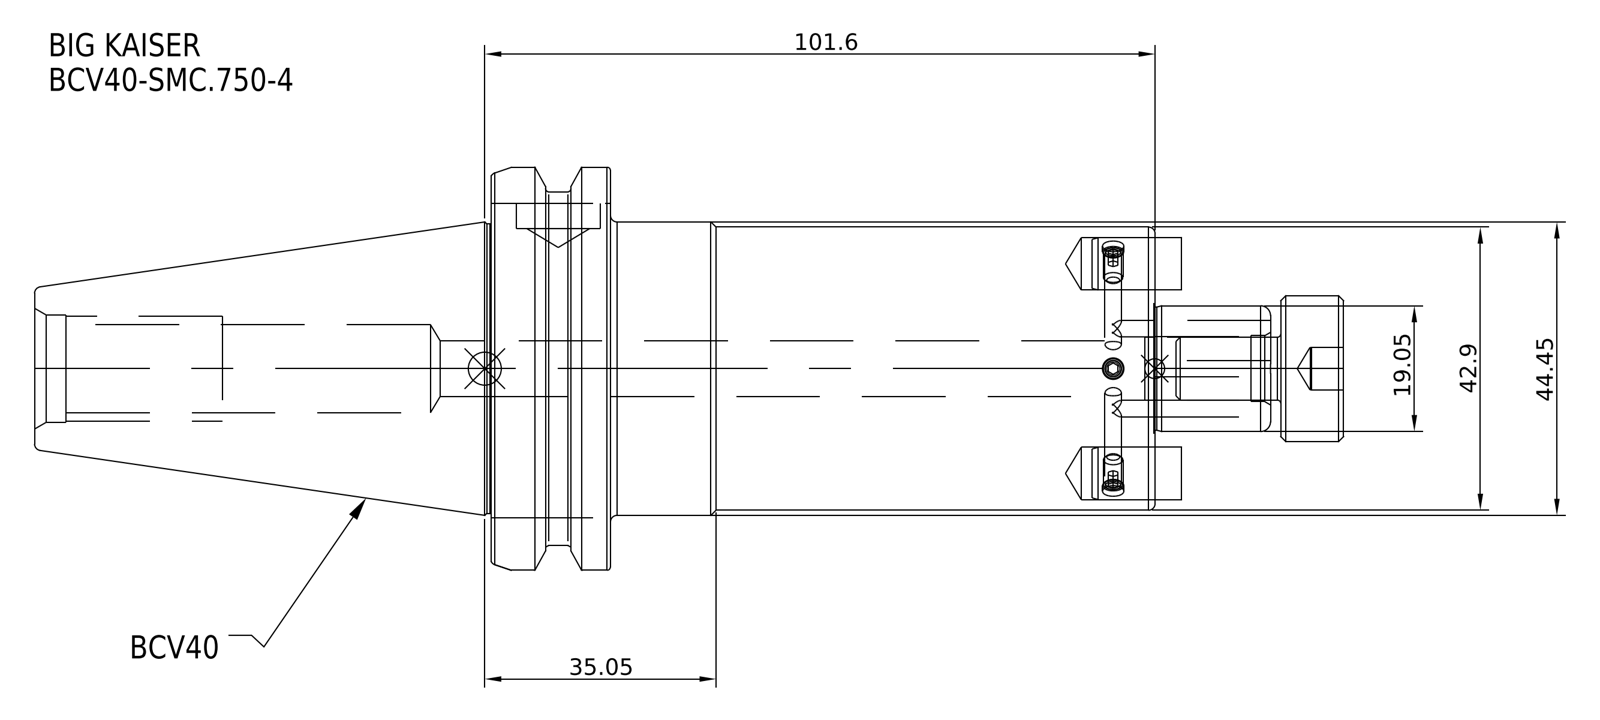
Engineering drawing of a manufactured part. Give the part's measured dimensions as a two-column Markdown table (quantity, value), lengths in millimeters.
| quantity | value |
| --- | --- |
| part name | BCV40-SMC_750-4 |
| STEP written by | SolidWorks 2021 (CONFIG_CONTROL_DESIGN) |
| units | millimeters |
| bodies | 1 solid, 38 faces (18 planar, 14 cylindrical, 6 other) |
| overall size | 173.82 × 63.5 × 63.5 |
| volume | 238 637 mm³ |
| surface area | 30 472 mm² |
| round holes (diameter × count) | 8.43 × 1 |
| round bosses / shafts (diameter × count) | 63.5 × 1, 56.36 × 1, 44.45 × 1, 42.9 × 1 |
| main face-to-face distances | 18.05, 82.55, 100.6, 169.85, 87.3, 69.25, 66.55, 16, 34.05, 103.3 |
